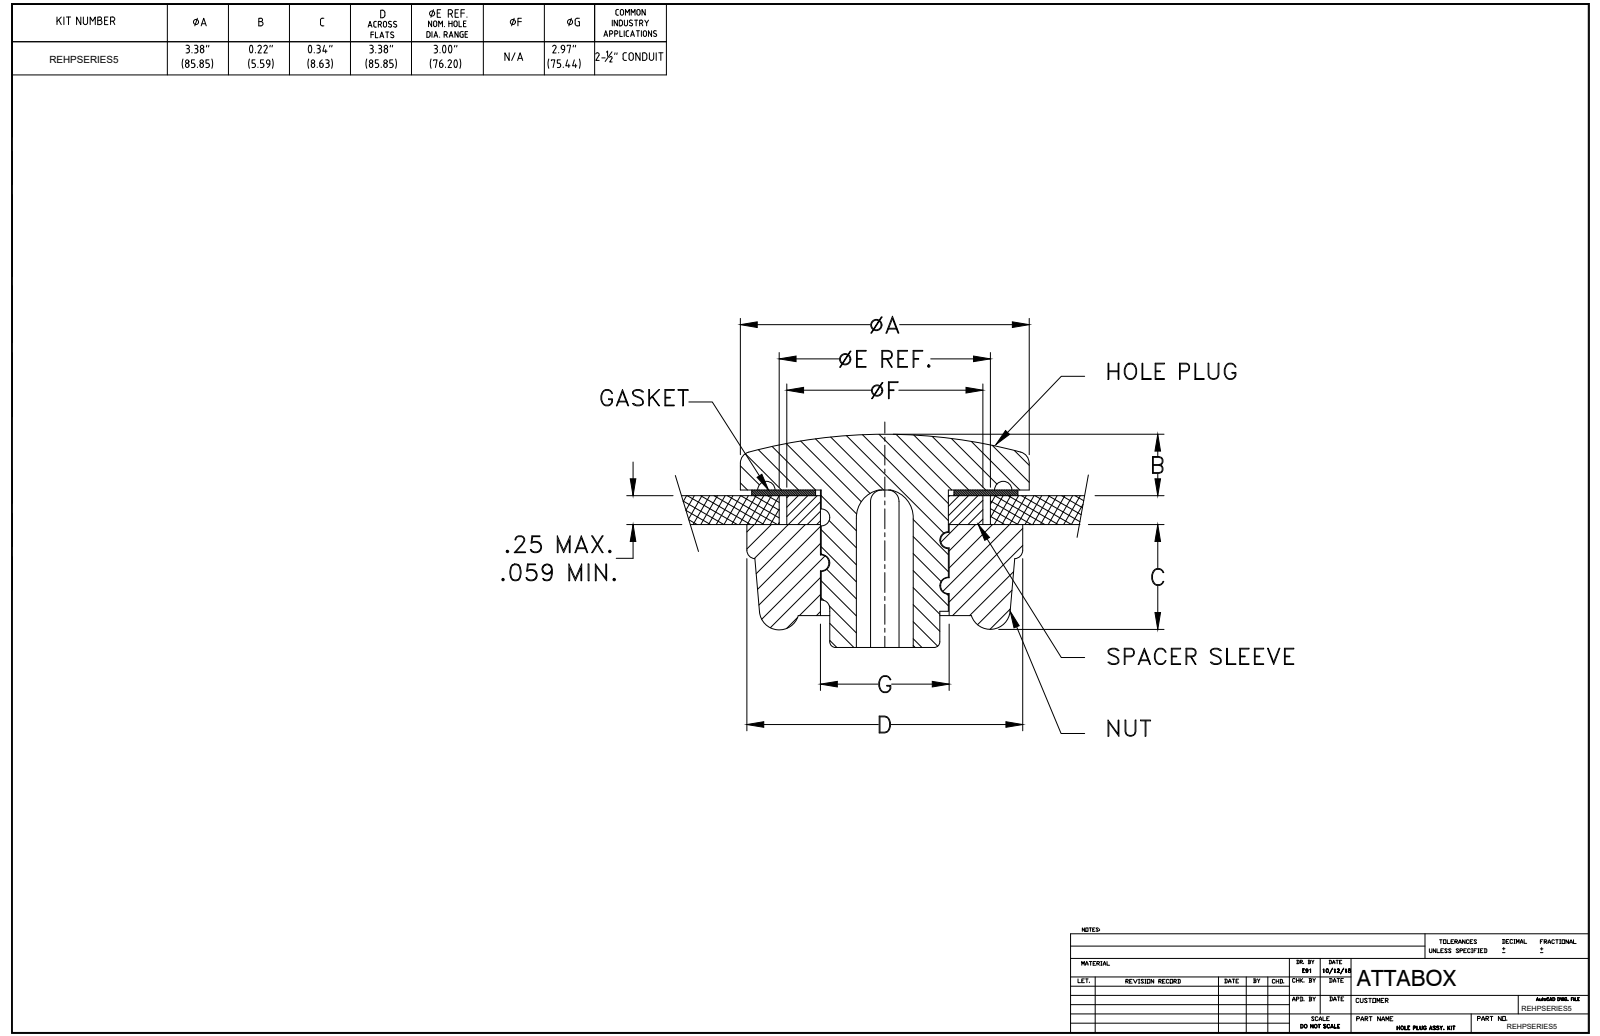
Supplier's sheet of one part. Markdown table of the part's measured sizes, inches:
| quantity | value |
| --- | --- |
| part name | HPSERIES5 |
| STEP written by | SolidWorks 2018 (AUTOMOTIVE_DESIGN) |
| units | inches |
| bodies | 3 solids, 171 faces (37 planar, 55 cylindrical, 79 other) |
| overall size | 3.679 × 3.572 × 1.13 |
| volume | 6.321 in³ |
| surface area | 49.78 in² |
| round holes (diameter × count) | 2.97 × 1, 2.99 × 1 |
| round bosses / shafts (diameter × count) | 3.38 × 1, 3.35 × 1, 3.26 × 1, 2.91 × 1 |
| partial cylindrical surfaces (radius × count) | 0.01 × 8, 0.04 × 8, 0.08 × 8, 0.03 × 6, 0.59 × 6, 0.009 × 4, 0.13 × 2 |
| main face-to-face distances | 0.03, 0.72, 0.75, 0.506, 0.214, 0.244, 1.96, 0.631, 0.125, 0.089 |
